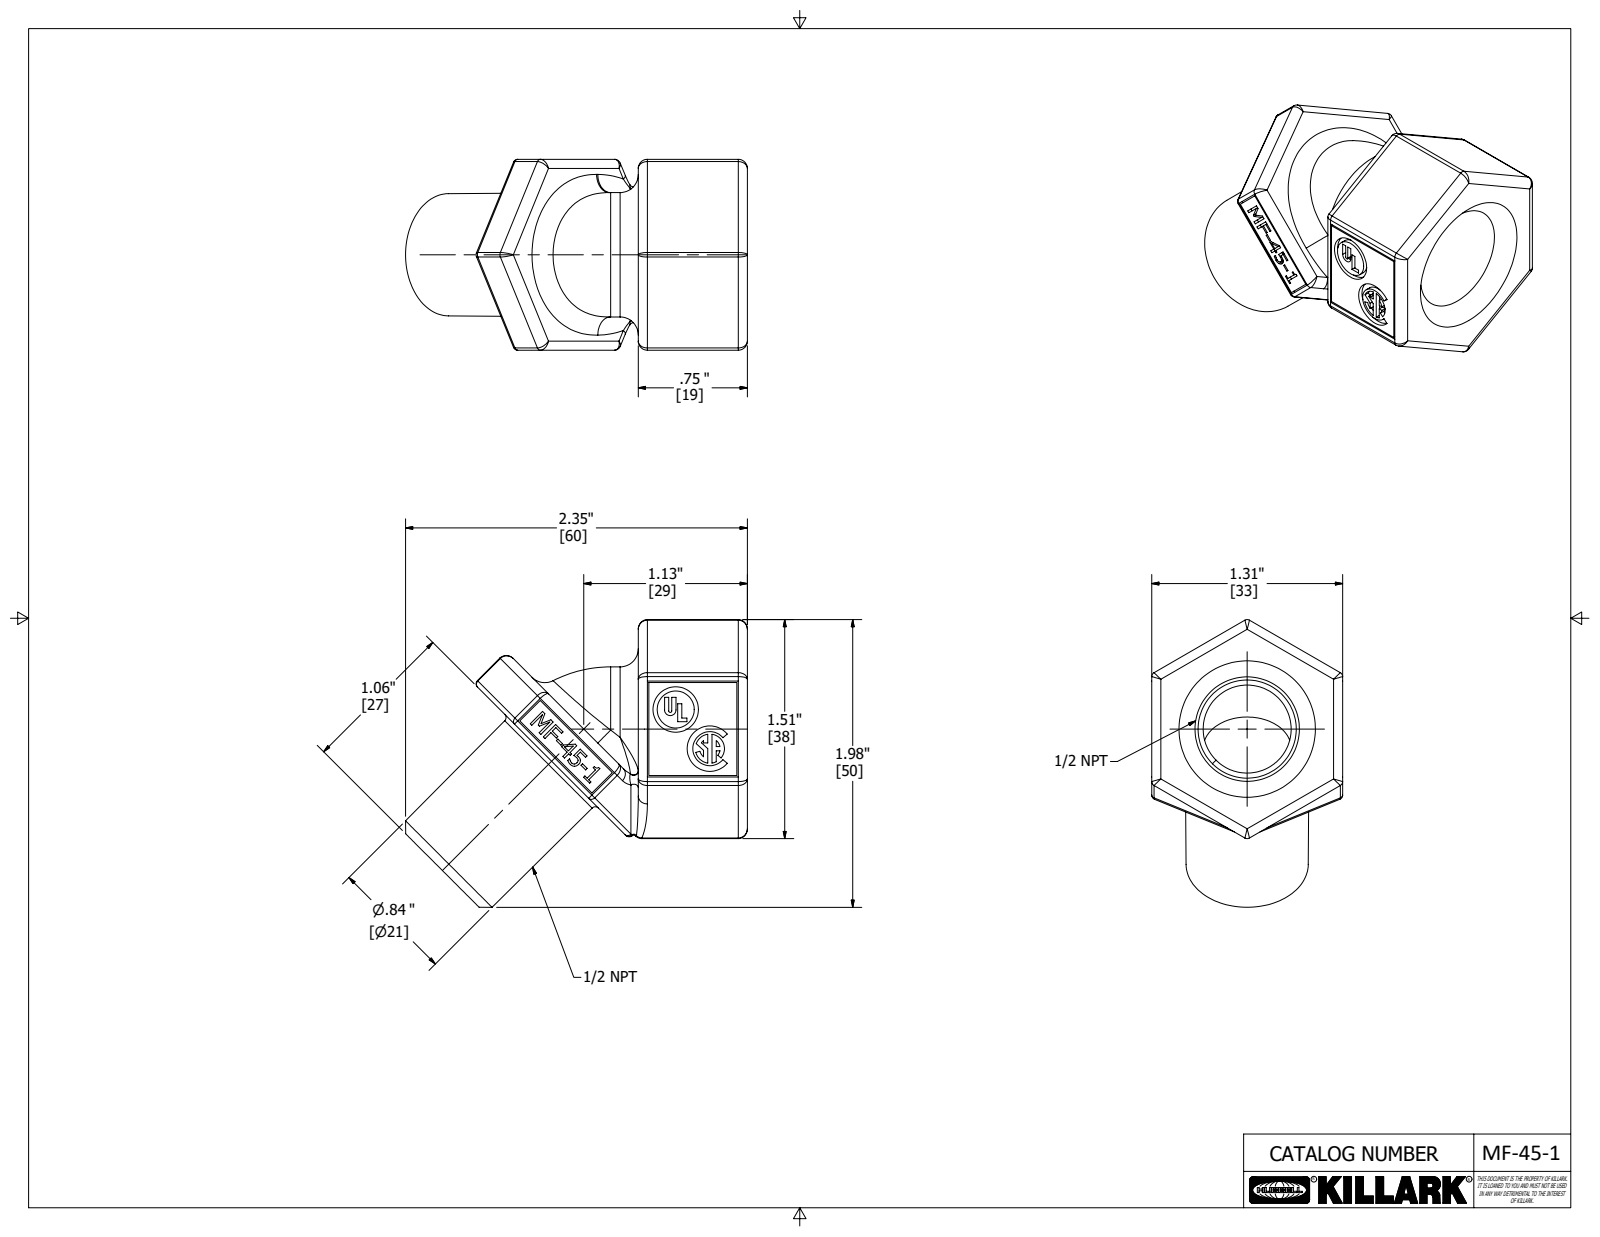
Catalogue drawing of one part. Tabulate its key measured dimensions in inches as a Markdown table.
| quantity | value |
| --- | --- |
| part name | MF-45-1 |
| STEP written by | Autodesk Inventor 2020 (AUTOMOTIVE_DESIGN) |
| units | inches |
| bodies | 1 solid, 650 faces (410 planar, 51 cylindrical, 189 other) |
| overall size | 2.35 × 1.978 × 1.313 |
| volume | 1.549 in³ |
| surface area | 17.45 in² |
| round holes (diameter × count) | 0.313 × 1 |
| round bosses / shafts (diameter × count) | 0.255 × 1 |
| partial cylindrical surfaces (radius × count) | 0.031 × 19, 0.062 × 18, 0.01 × 1, 0.039 × 1, 0.071 × 1, 0.1 × 1, 0.117 × 1, 0.156 × 1 |
| main face-to-face distances | 1.313, 0.032, 1.281, 0.313, 1.312, 0.75, 1.062, 1.375, 1.249, 0.063 |
